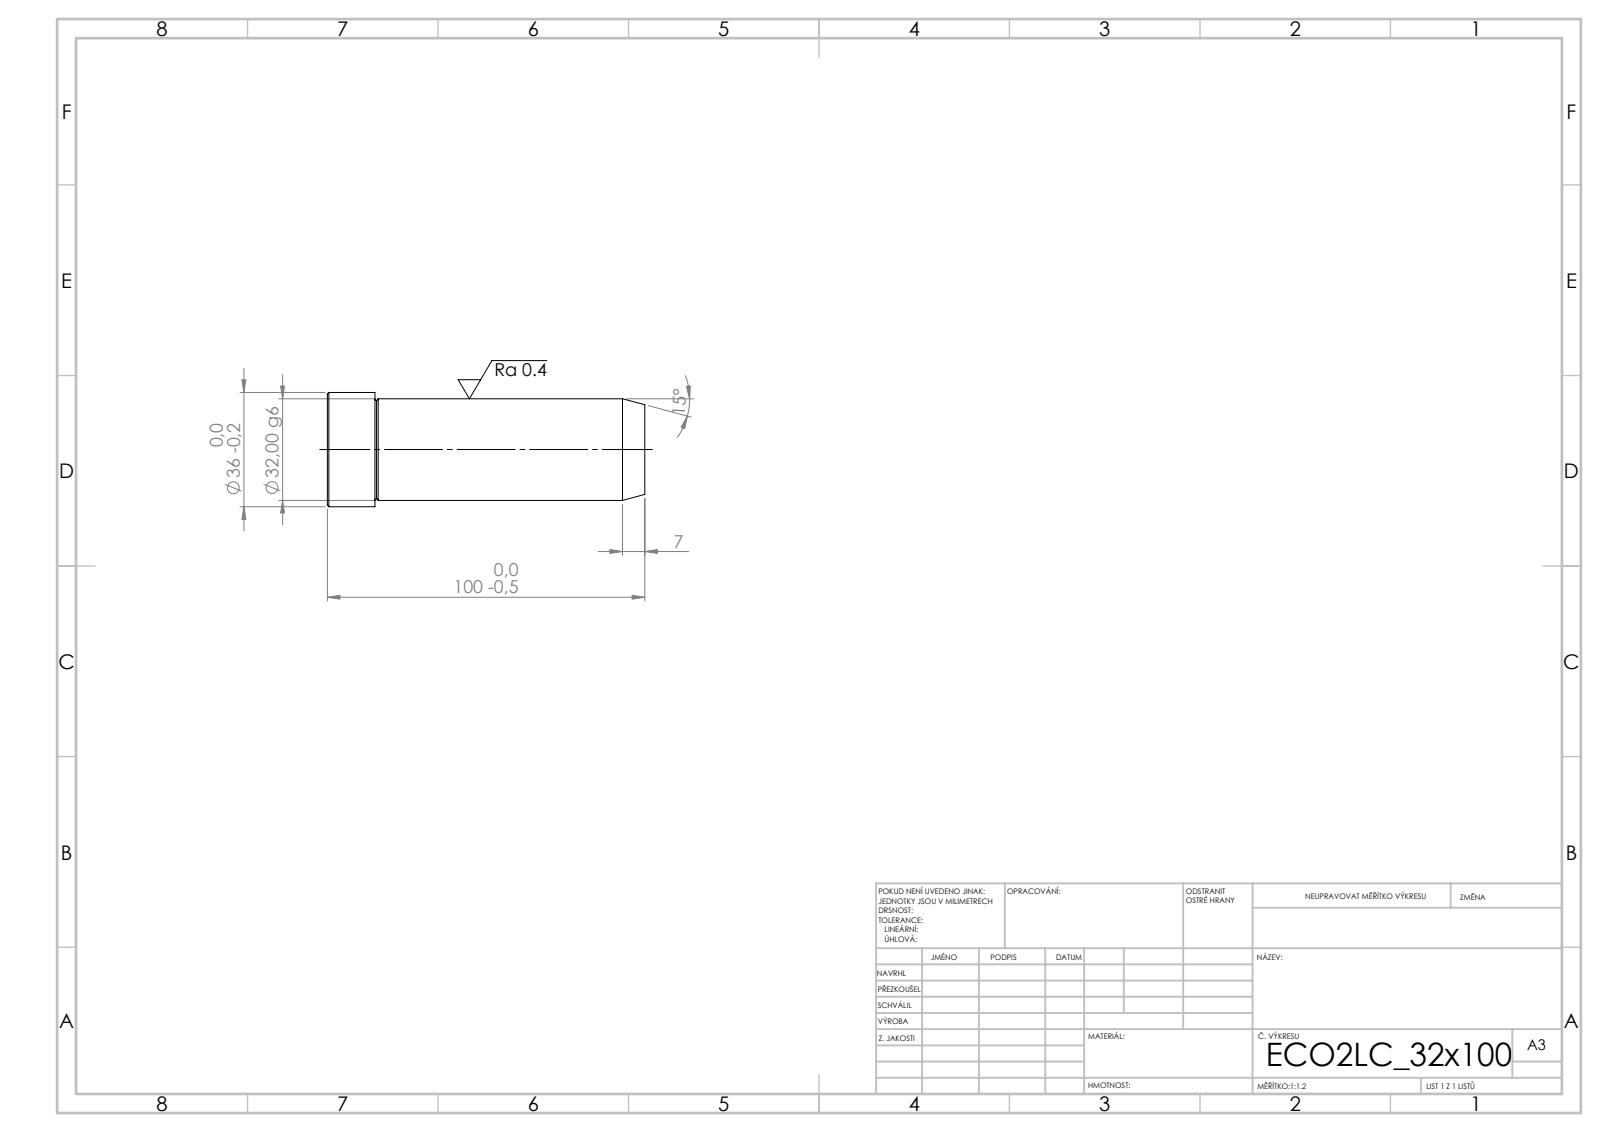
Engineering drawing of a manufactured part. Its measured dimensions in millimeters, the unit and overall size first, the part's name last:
Units: millimetres
Overall size (bounding box): 100 × 36 × 36
Round bosses / shafts (diameter × count): ⌀36 ×1, ⌀32 ×1
Main face-to-face distances: 100, 85, 15
Volume: 82 942 mm³ · Surface area: 12 103 mm²
Bodies: 1 solid, 15 faces (3 planar, 4 cylindrical, 8 other)
STEP written by: SolidWorks 2019 (CONFIG_CONTROL_DESIGN)
